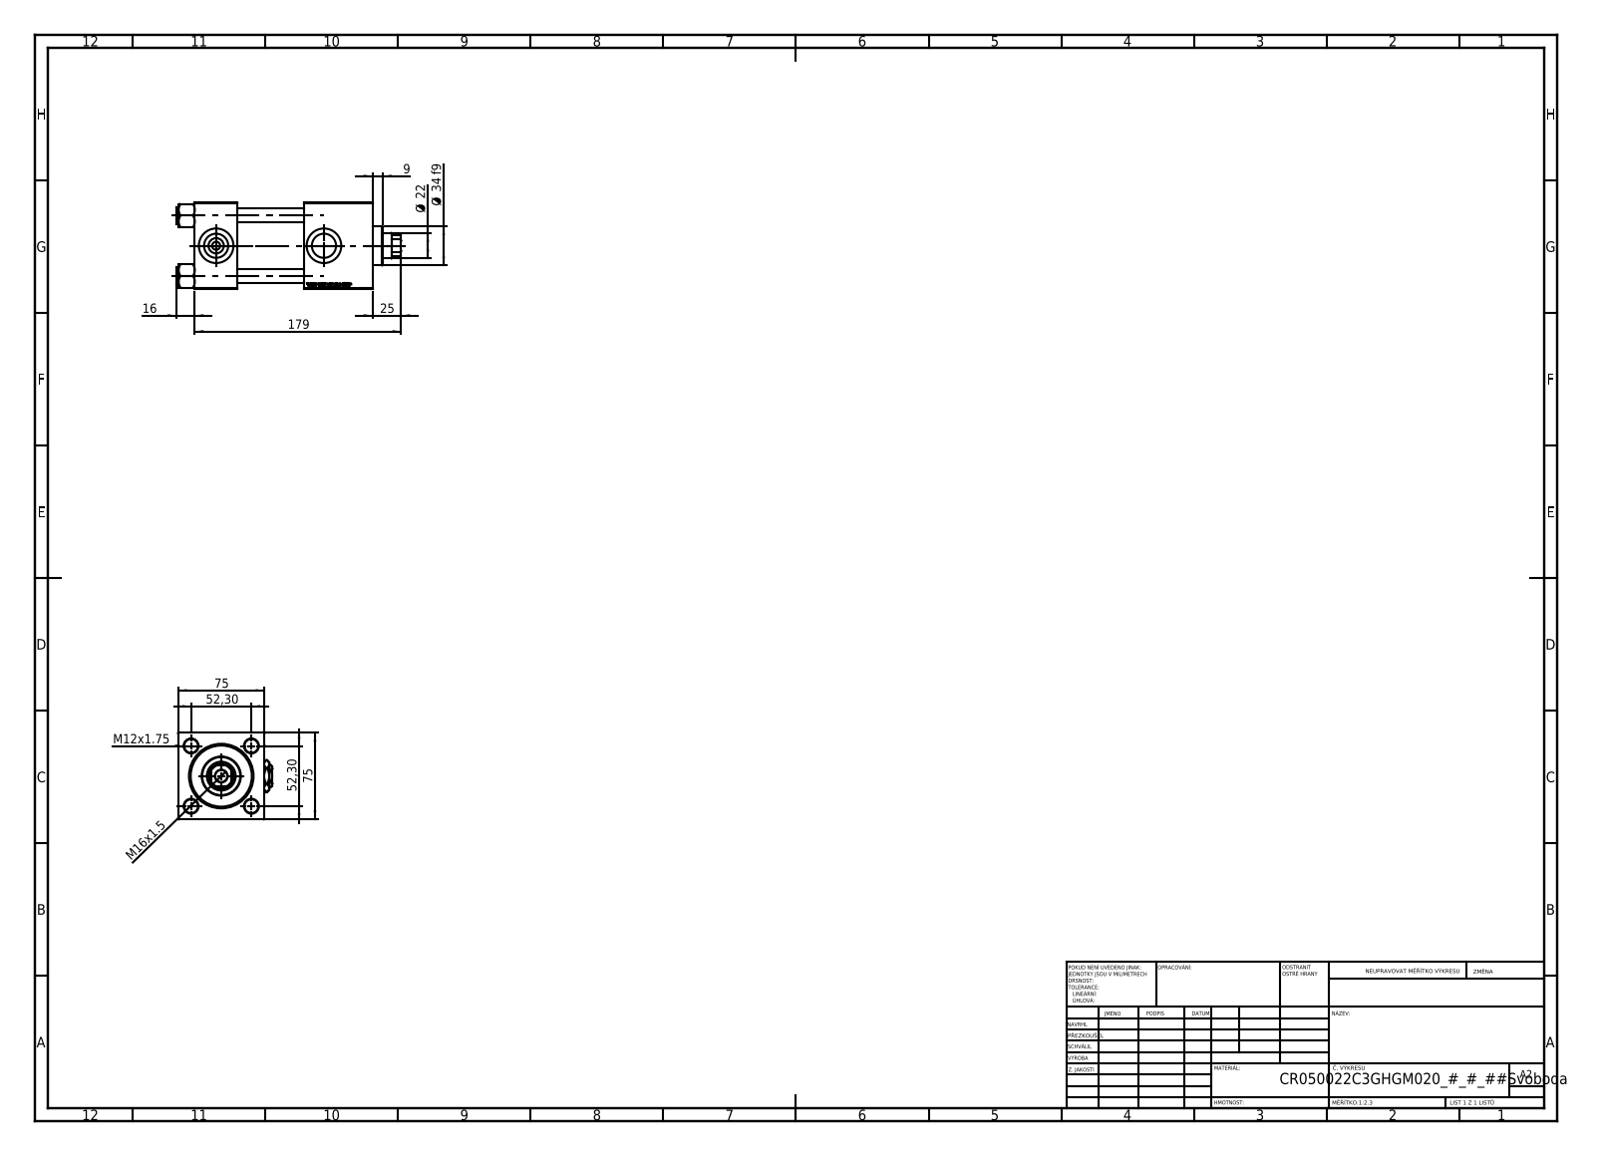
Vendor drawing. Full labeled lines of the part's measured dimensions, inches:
Part name (STEP PRODUCT): Zatka_pro_OIL_PORT; V215CR_VCP_C; NUT_M5_C; V215CR_C_Body (+2 more)
STEP written by: SolidWorks 2019 (CONFIG_CONTROL_DESIGN)
Units: inches
Bodies: 13 solids, 1249 faces (573 planar, 98 cylindrical, 578 other)
Overall size (bounding box): 7.677 × 3.239 × 2.953
Volume: 39.78 in³ · Surface area: 235.2 in²
Round holes (diameter × count): ⌀0.472 ×4, ⌀0.276 ×2, ⌀0.825 ×2, ⌀1.181 ×2, ⌀0.413 ×1, ⌀0.866 ×1, ⌀0.984 ×1, ⌀1.614 ×1, ⌀1.969 ×1, ⌀2.087 ×1
Round bosses / shafts (diameter × count): ⌀0.591 ×4, ⌀2.205 ×1, ⌀1.339 ×1
Partial cylindrical surfaces — rounded edges, fillets, slot ends (radius × count): R0.413 ×1
Main face-to-face distances: 2.953, 1.457, 6.063, 4.606, 3.74, 2.283, 2.323, 4.933, 3.476, 1.193
Hole centre spacings: 1.456, 2.059, 2.912, 3.681
